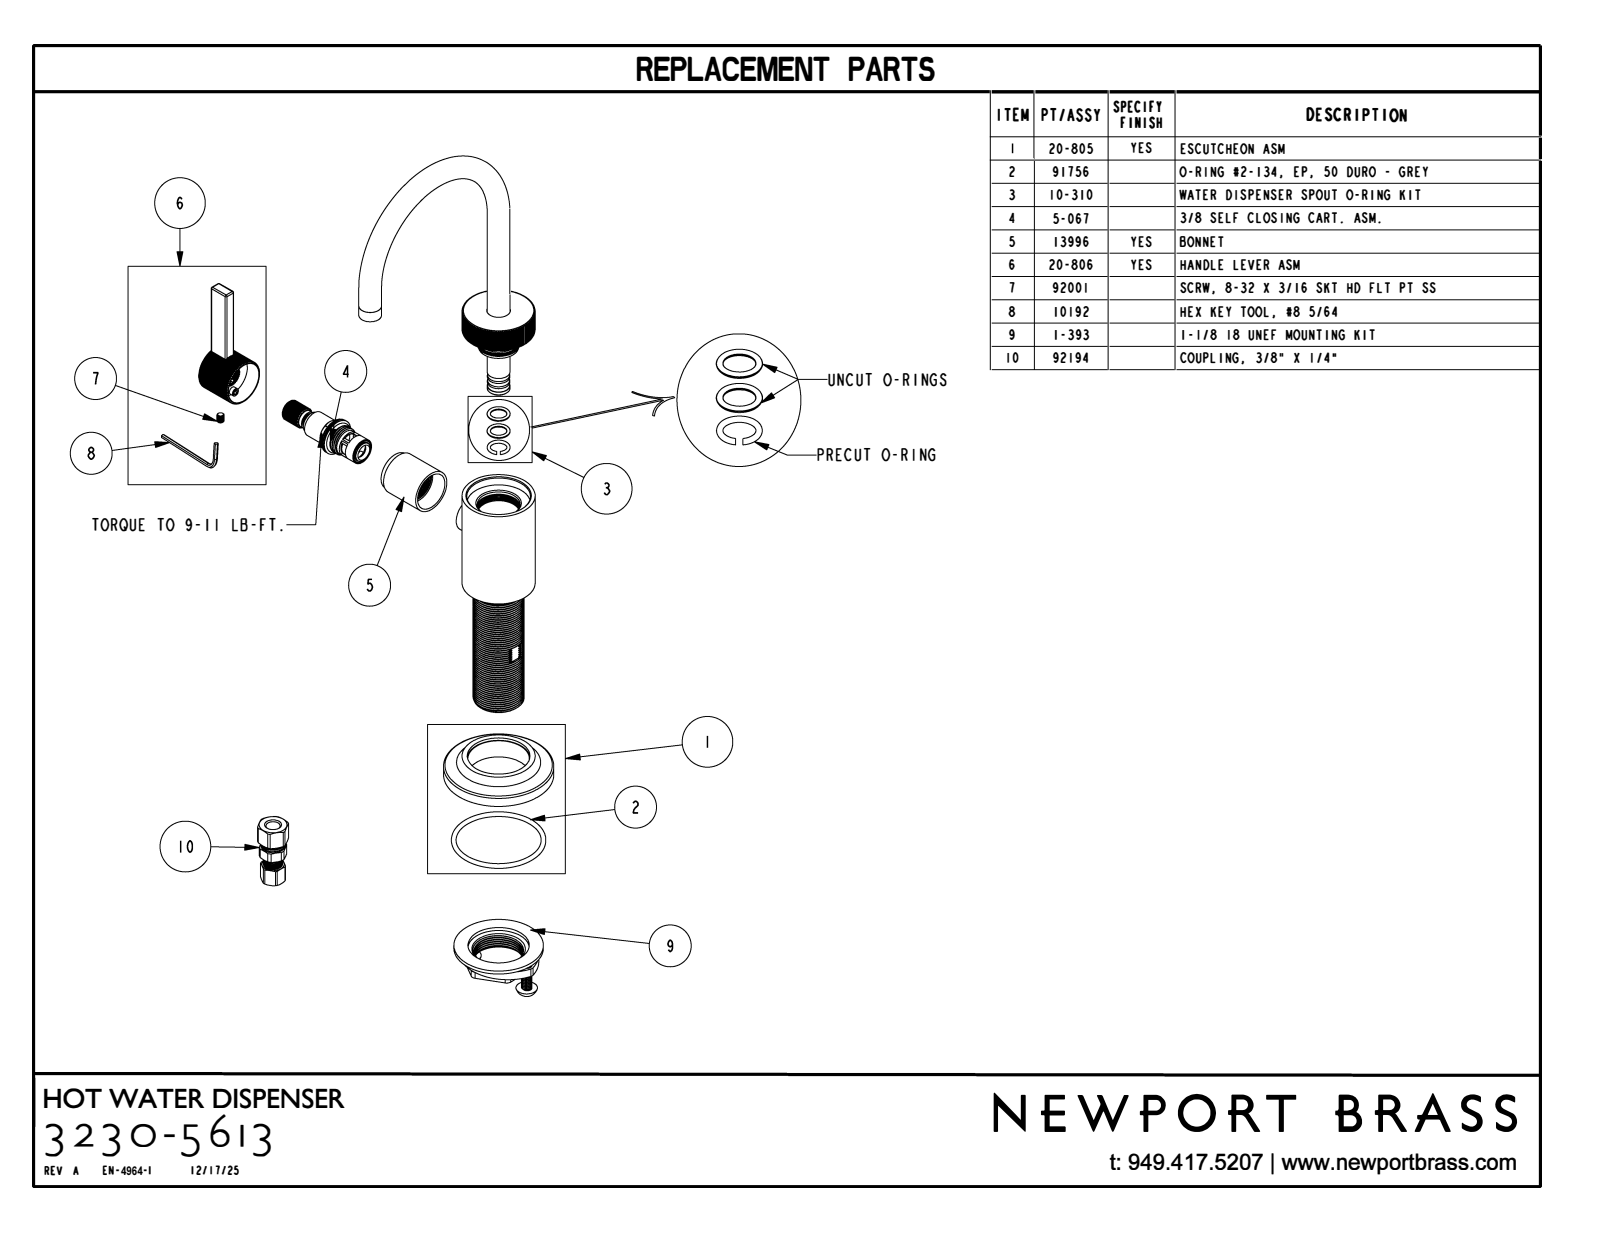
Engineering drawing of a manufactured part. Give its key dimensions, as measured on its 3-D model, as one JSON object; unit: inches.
{"part_name": "3230-5613", "step_written_by": "CREO PARAMETRIC BY PTC INC, 2023134 (CONFIG_CONTROL_DESIGN)", "units": "inches", "bodies": {"solids": 1, "faces": 710, "planar": 412, "cylindrical": 248, "other": 50}, "overall_size": [9.4, 5.465, 3.716], "volume_in3": 9.919, "surface_area_in2": 70.65, "round_holes": [[0.067, 4], [0.4, 2], [0.2, 1], [0.253, 1], [0.37, 1], [0.52, 1], [0.615, 1], [1, 1]], "round_bosses_or_shafts": [[0.5, 2], [2.43, 1], [1.61, 1], [0.97, 1], [0.875, 1], [0.38, 1]], "partial_cylinders_radius": [[0.03, 12], [0.06, 2], [0.515, 1]], "face_to_face_distances": [3.381, 0.257, 0.25, 0.71, 0.711, 0.48, 0.265, 1.088, 1.165, 3.246], "hole_center_spacings": [0.185, 0.262, 0.37, 4.004, 3.815, 4, 4.185]}
